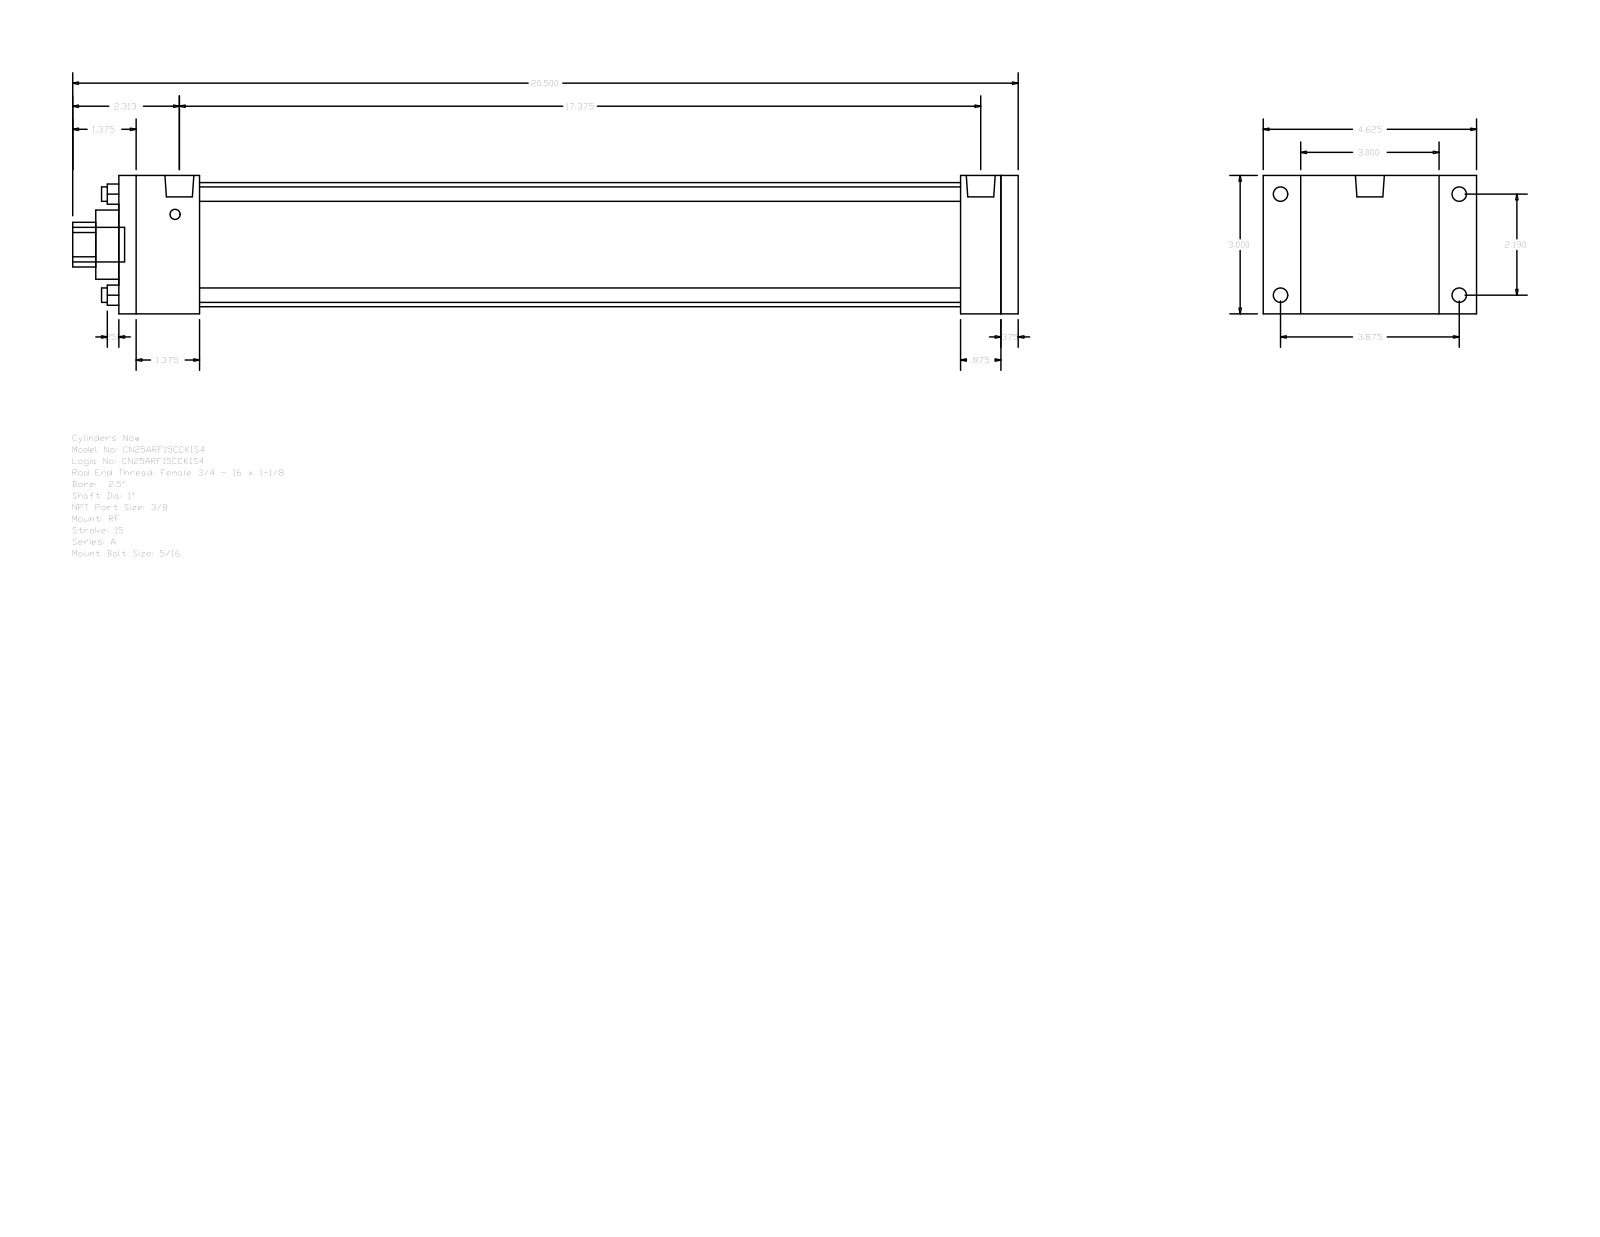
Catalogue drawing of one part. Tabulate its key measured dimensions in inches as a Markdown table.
| quantity | value |
| --- | --- |
| part name | A_RF__0250_1 |
| STEP written by | GSSL Pune (CONFIG_CONTROL_DESIGN) |
| units | inches |
| bodies | 0 solids, 92 faces (64 planar, 28 cylindrical, 0 other) |
| overall size | 20.5 × 4.625 × 3 |
| round holes (diameter × count) | 0.313 × 4, 1 × 1, 1.5 × 1, 2.69 × 1 |
| round bosses / shafts (diameter × count) | 0.313 × 4, 0.219 × 4, 0.627 × 2, 0.75 × 1 |
| partial cylindrical surfaces (radius × count) | 0.484 × 1 |
| main face-to-face distances | 3, 19.5, 0.375, 19.125, 1.75, 18.25, 16.5, 17.375, 17.75, 0.875 |
| hole center spacings | 1.548, 2.19, 3.097 |
